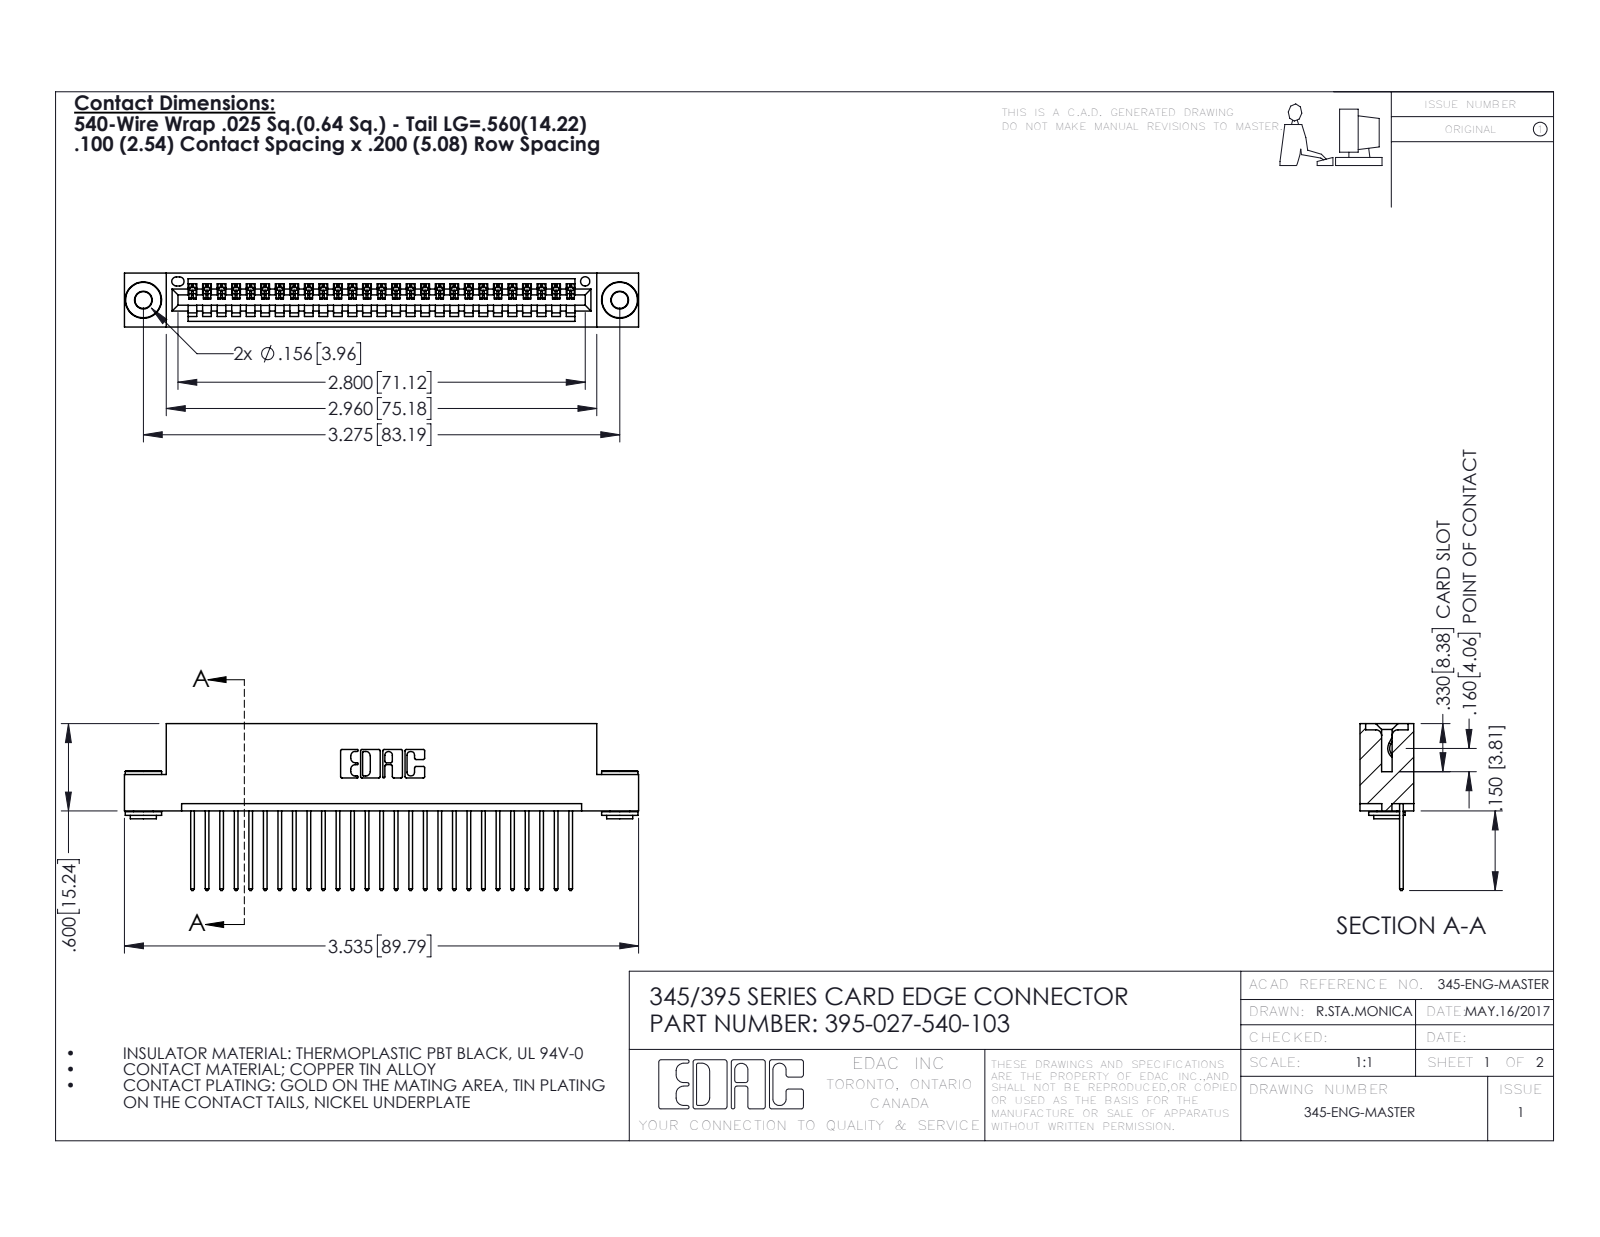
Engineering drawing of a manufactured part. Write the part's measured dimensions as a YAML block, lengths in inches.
part_name: "345 Part_Flush Mounting Lugs - 0.156 Dia-TH; 345-250-002_345-250-002-102; 395-027-540-103; 345-292-001_345-293-140"
step_written_by: "SolidWorks 2016 (CONFIG_CONTROL_DESIGN)"
units: inches
bodies: {solids: 30, faces: 1730, planar: 1170, cylindrical: 552, other: 8}
overall_size: [3.535, 1.147, 0.37]
volume: 0.516
surface_area: 17.85
round_holes:
  - {diameter: 0.116, count: 2}
  - {diameter: 0.156, count: 2}
  - {diameter: 0.064, count: 1}
round_bosses_or_shafts:
  - {diameter: 0.25, count: 2}
  - {diameter: 0.18, count: 2}
  - {diameter: 0.136, count: 2}
partial_cylinders:
  - {radius: 0.006, count: 54}
  - {radius: 0.01, count: 54}
  - {radius: 0.01, count: 22}
  - {radius: 0.007, count: 6}
  - {radius: 0.031, count: 6}
  - {radius: 0.026, count: 3}
  - {radius: 0.031, count: 2}
  - {radius: 0.04, count: 2}
face_to_face_distances: [0.072, 0.298, 0.2, 0.37, 0.025, 0.098, 0.272, 0.225, 0.149, 0.072]
hole_center_spacings: [0.27, 3.04, 3.275]
